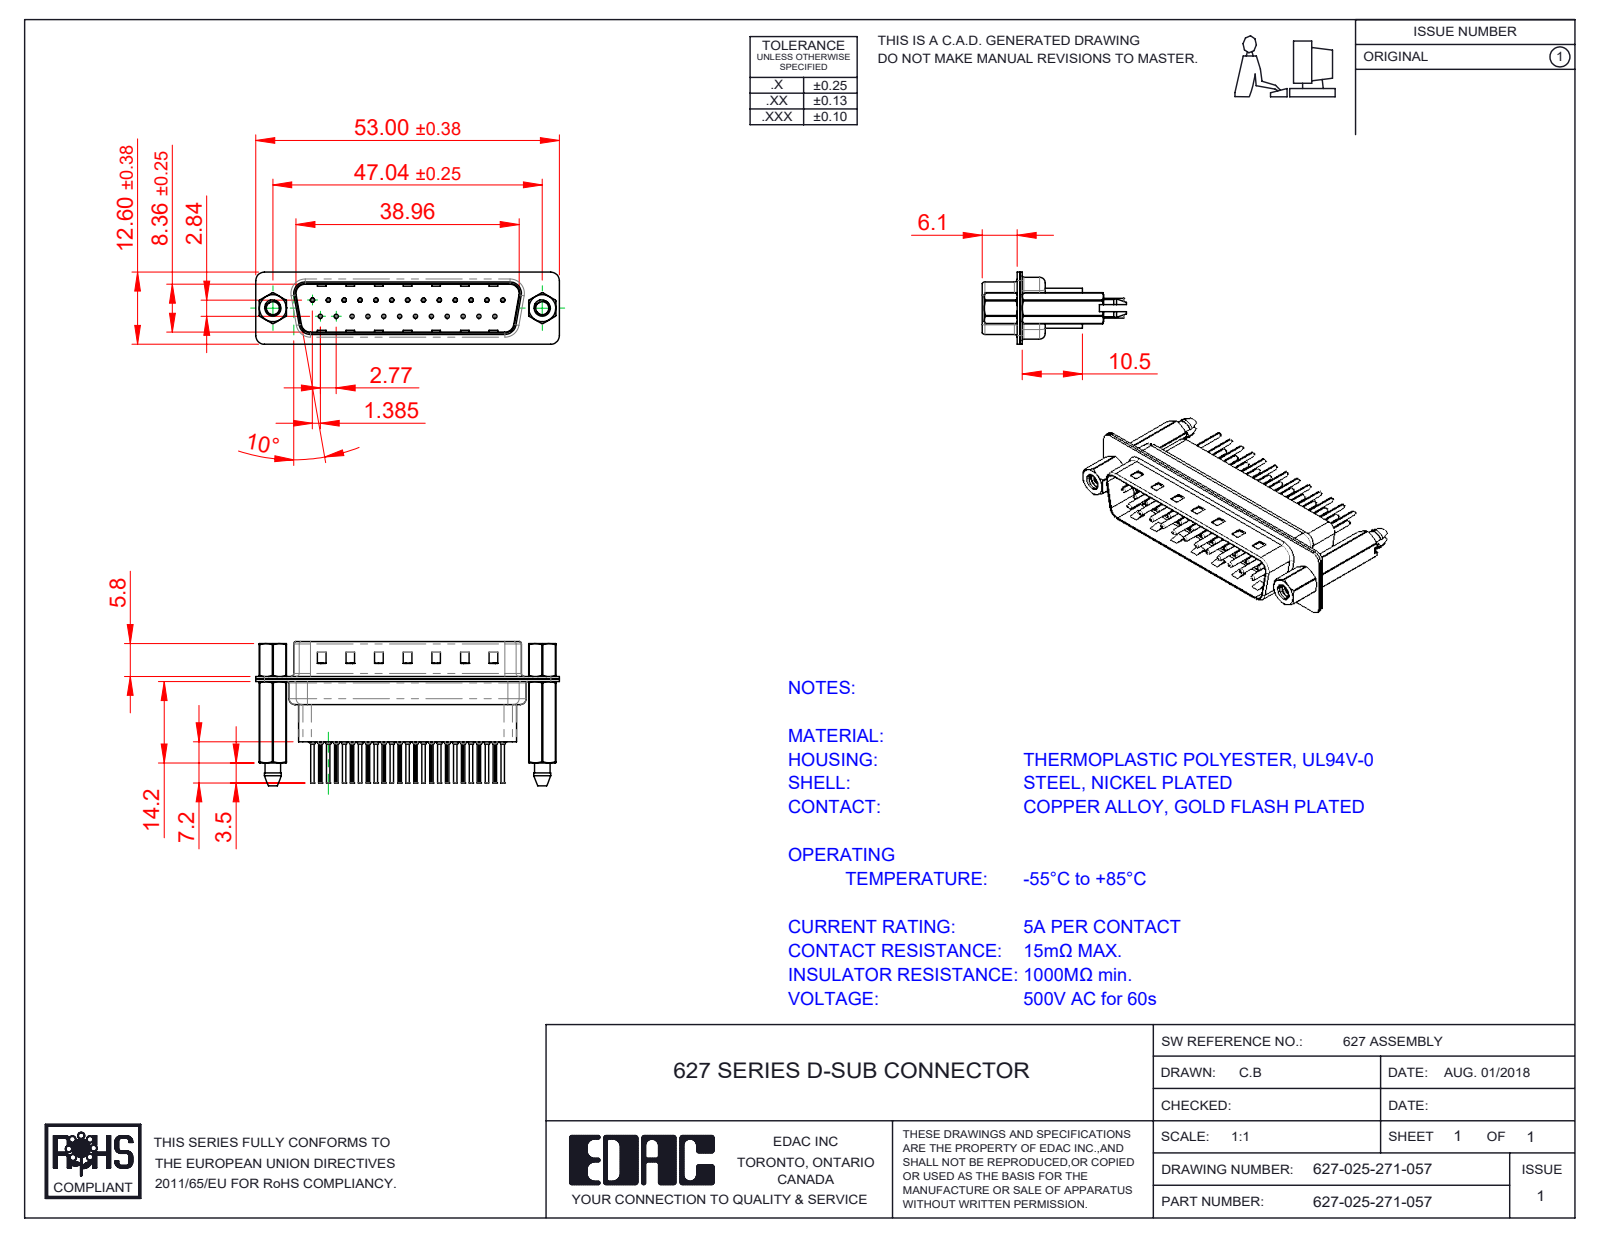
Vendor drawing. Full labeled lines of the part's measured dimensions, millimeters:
Part name (STEP PRODUCT): 627 Shell Front_25 Contacts; 627-025-271-057; 627 4-40 Hex Standoff; 627 Contact Row 1_61 (+4 more)
STEP written by: SolidWorks 2020 (CONFIG_CONTROL_DESIGN)
Units: millimetres
Bodies: 32 solids, 3060 faces (825 planar, 1200 cylindrical, 1035 other)
Overall size (bounding box): 53 × 25.1 × 12.6
Volume: 4 392 mm³ · Surface area: 11 276 mm²
Round holes (diameter × count): ⌀0.2 ×25, ⌀0.35 ×25, ⌀1.1 ×25, ⌀1.6 ×25, ⌀2.26 ×2, ⌀2.29 ×2, ⌀4 ×2, ⌀4.8 ×2
Round bosses / shafts (diameter × count): ⌀2 ×25, ⌀1.5 ×25, ⌀0.75 ×25, ⌀0.6 ×25, ⌀4.9 ×2, ⌀2.79 ×2
Partial cylindrical surfaces — rounded edges, fillets, slot ends (radius × count): R0.1 ×50, R1.5 ×18, R2 ×12, R1.6 ×10, R0.5 ×8, R0.25 ×4, R0.6 ×4, R0.65 ×4
Main face-to-face distances: 0.4, 0.45, 0.82, 9.58, 0.68, 7.68, 1.5, 0.9, 1.08, 8.08
Hole centre spacings: 3.16, 8.31, 2.77, 5.54, 11.08, 16.62, 5.03, 5.04
